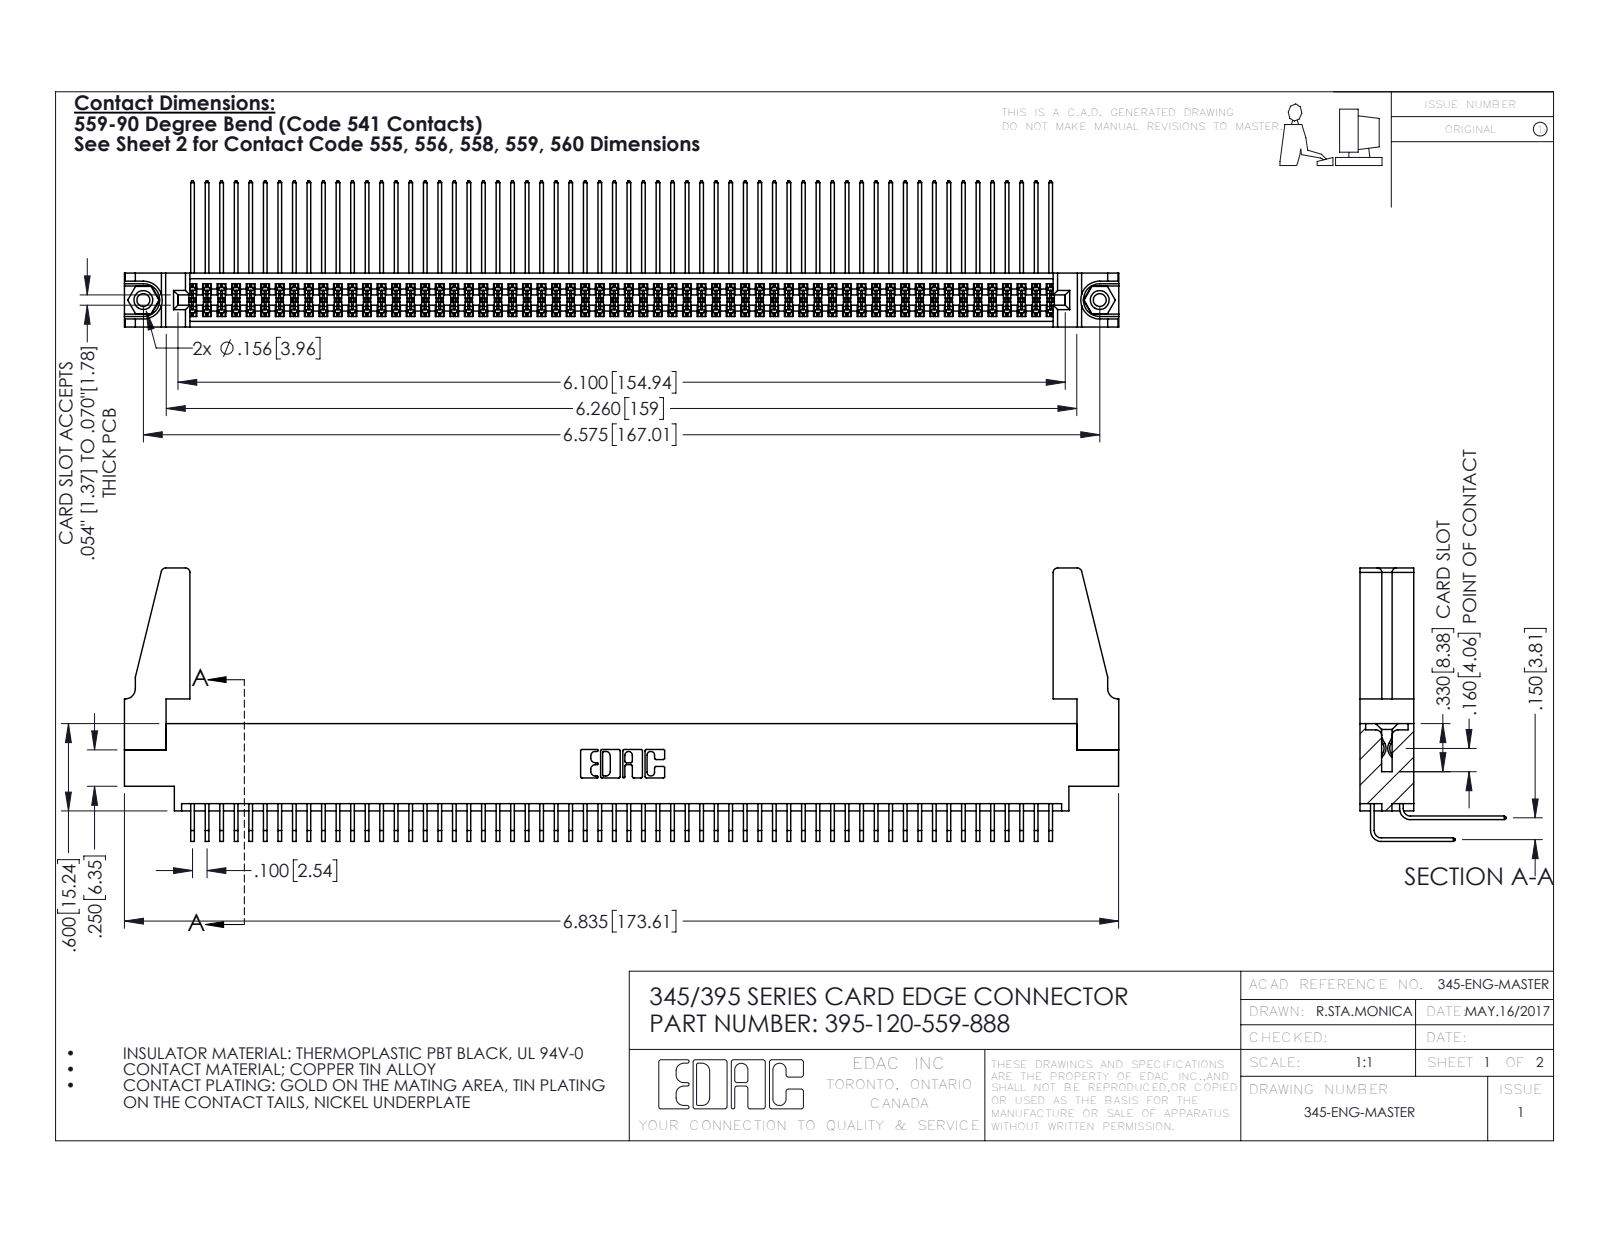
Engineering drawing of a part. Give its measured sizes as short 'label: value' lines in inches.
name: 345-292-001_559 Tail - 2; 395-120-559-888; 345-292-001_558 559 Tail - 1; 345-250-001_345-250-001-102 (+2 more)
written by: SolidWorks 2016 (CONFIG_CONTROL_DESIGN)
unit: in
bodies: 125 solids, 6494 faces (4356 planar, 2122 cylindrical, 16 other)
size: 6.836 × 1.879 × 1.005
volume: 1.273 in³; area: 51 in²
holes: 2× ⌀0.089, 2× ⌀0.125, 2× ⌀0.156, 1× ⌀0.064
bosses: 2× ⌀0.155
rounds: 180× R0.006, 22× R0.01, 8× R0.03, 6× R0.007, 6× R0.031, 3× R0.026, 2× R0.014, 2× R0.019
face distances: 0.072, 0.298, 0.37, 0.098, 0.272, 0.025, 0.2, 0.225, 0.15, 0.175
hole spacings: 0.27, 6.339, 6.575
